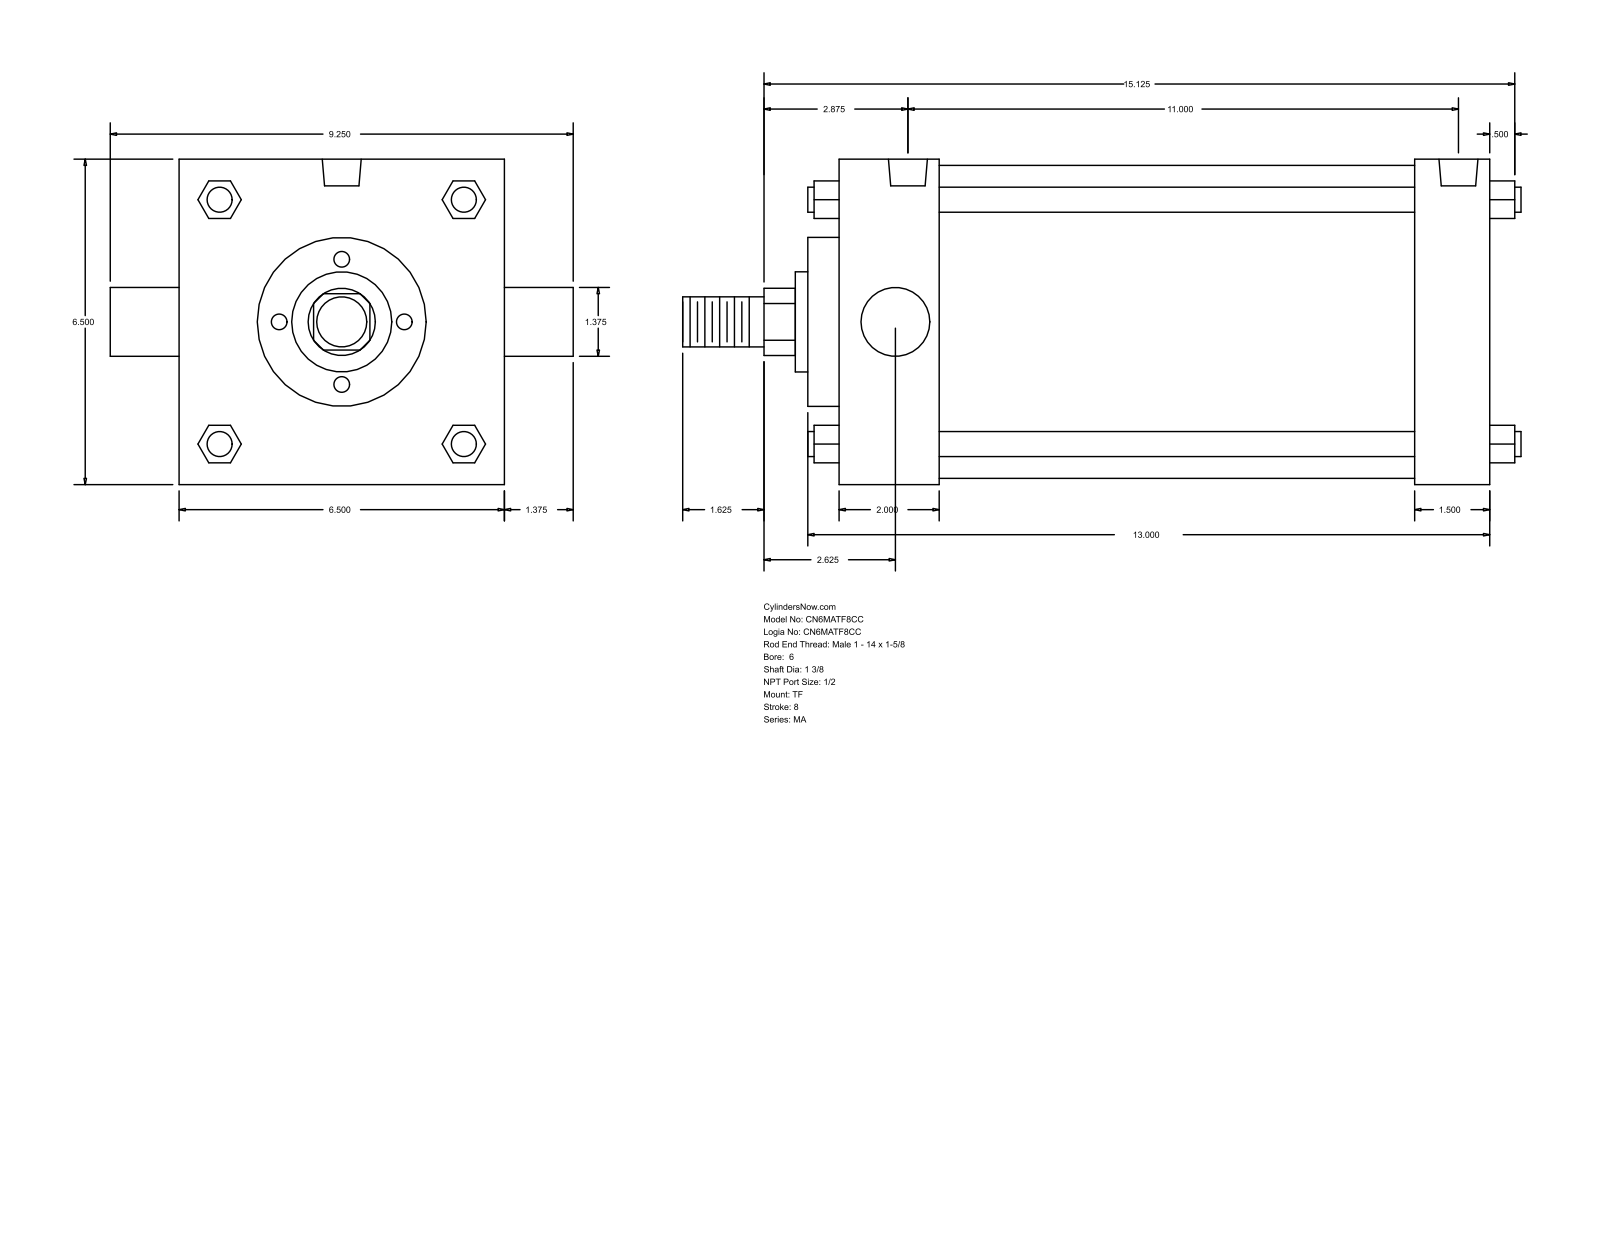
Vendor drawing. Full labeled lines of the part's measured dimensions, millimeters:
Part name (STEP PRODUCT): MA_TF__0600_1.375
STEP written by: GSSL Pune (CONFIG_CONTROL_DESIGN)
Units: millimetres
Bodies: 0 solids, 122 faces (93 planar, 29 cylindrical, 0 other)
Overall size (bounding box): 425.45 × 234.95 × 165.1
Round holes (diameter × count): ⌀17.46 ×3, ⌀19.77 ×2
Round bosses / shafts (diameter × count): ⌀12.7 ×4, ⌀34.92 ×2, ⌀158.75 ×1, ⌀85.72 ×1, ⌀50.8 ×1, ⌀25.4 ×1
Partial cylindrical surfaces — rounded edges, fillets, slot ends (radius × count): R17.06 ×1
Main face-to-face distances: 165.1, 333.38, 50.8, 295.28, 38.1, 282.58, 244.48, 66.67, 15.87, 311.15
Hole centre spacings: 3.18, 279.4, 282.58
